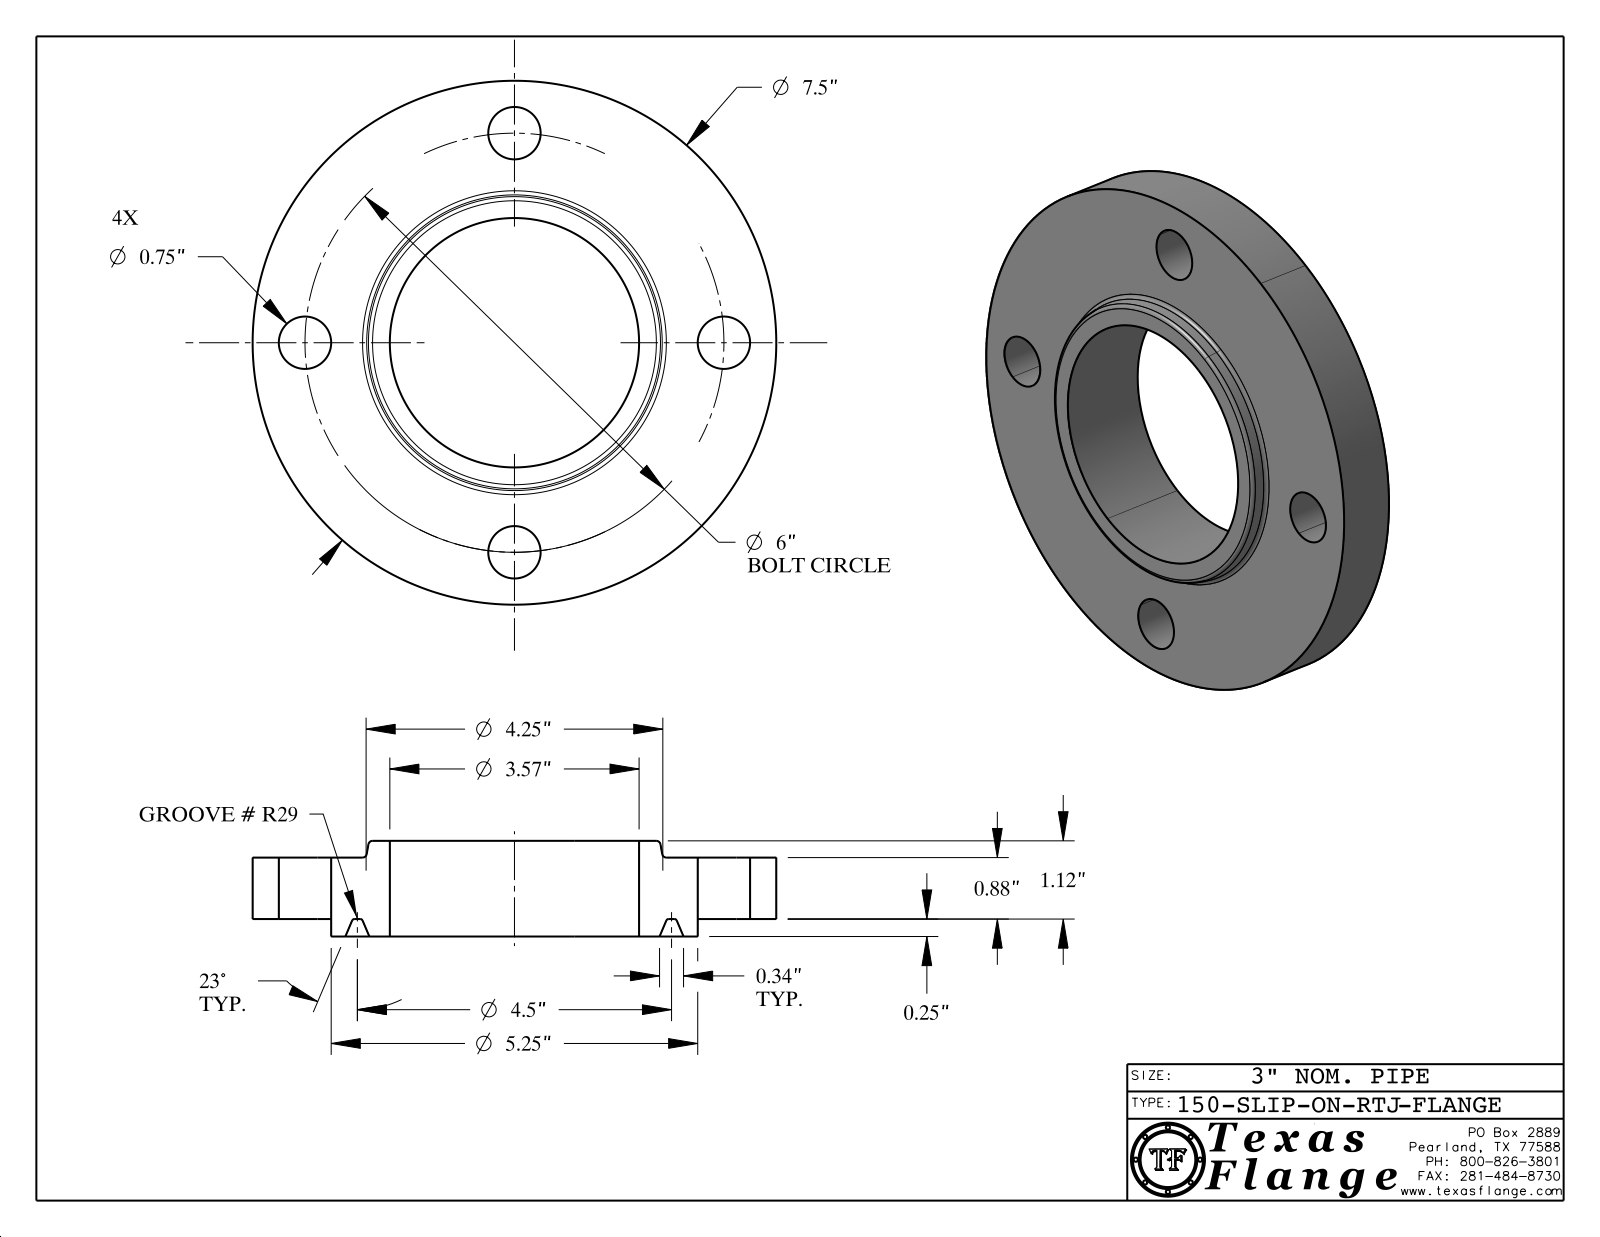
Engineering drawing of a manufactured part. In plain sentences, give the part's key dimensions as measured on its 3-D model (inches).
The part is named "150-SLIP-ON-RTJ". Its 3-D file was written by "CATIA V5 STEP AP214 (AUTOMOTIVE_DESIGN)". It is 1 solid with 419 faces: 371 planar, 34 cylindrical and 14 other. Overall it measures 7.5 by 7.5 by 1.37 inches. Its volume is 31.52 cubic inches and its surface area 120.2 square inches. Round holes: 4 of diameter 0.75, 1 of diameter 0.495, 1 of diameter 3.57. Round bosses or shafts: 8 of diameter 0.03, 1 of diameter 7.5, 1 of diameter 5.25, 1 of diameter 0.39. The main face-to-face distances are 0.88, 0.25, 1.13, 1.37, 1.12, 0.24, 1.115, 0.865, 0.015, 0.255. The hole center spacings are 3, 4.243, 2.296, 5.543, 6.
